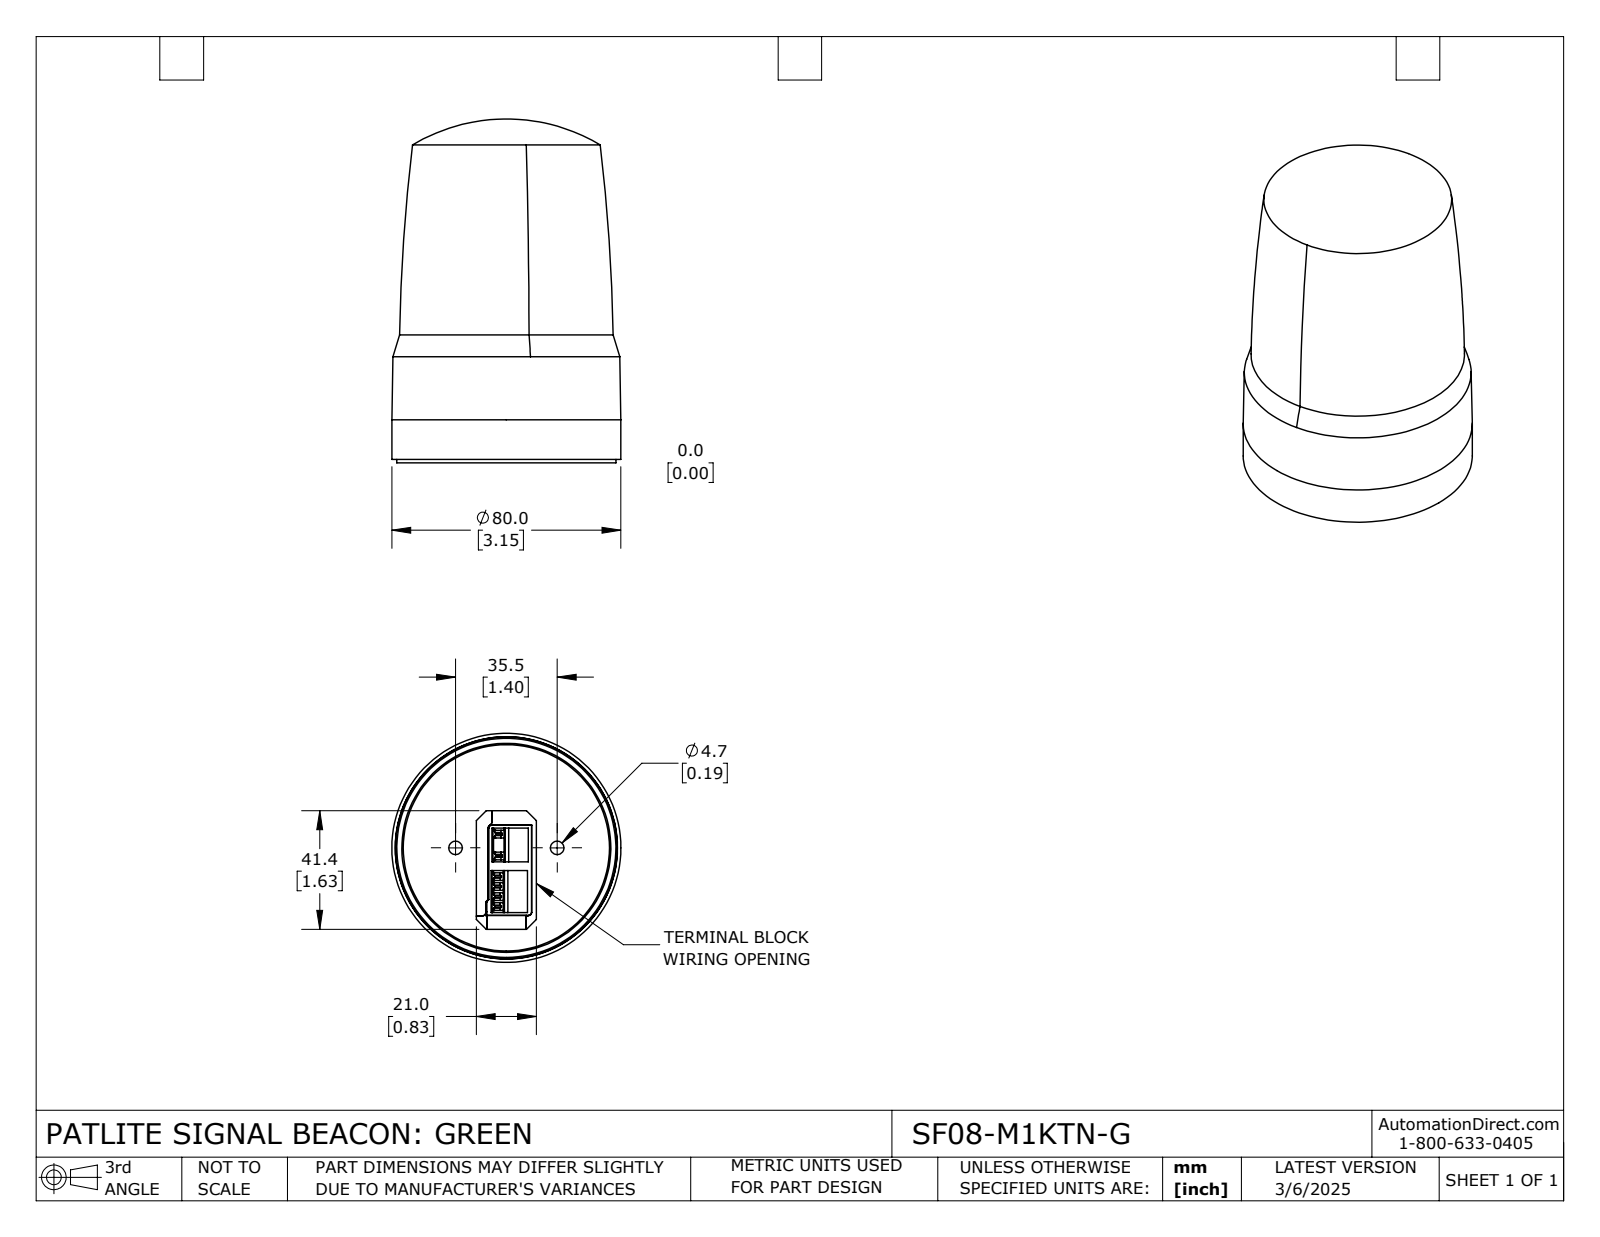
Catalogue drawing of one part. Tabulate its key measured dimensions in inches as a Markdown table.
| quantity | value |
| --- | --- |
| part name | SF08-M1KTN-G |
| STEP written by | SolidWorks 2024 (CONFIG_CONTROL_DESIGN) |
| units | inches |
| bodies | 2 solids, 287 faces (199 planar, 23 cylindrical, 65 other) |
| overall size | 4.724 × 3.15 × 3.15 |
| volume | 29.01 in³ |
| surface area | 81.21 in² |
| round holes (diameter × count) | 0.185 × 2, 0.48 × 2, 2.874 × 1 |
| round bosses / shafts (diameter × count) | 3.15 × 1, 3.012 × 1, 2.937 × 1, 2.835 × 1 |
| partial cylindrical surfaces (radius × count) | 1.319 × 1, 1.362 × 1 |
| main face-to-face distances | 0.248, 0.185, 0.433, 0.071, 0.504, 0.256, 0.059, 0.374, 0.126, 0.13 |
| hole center spacings | 0.699, 1.398 |
